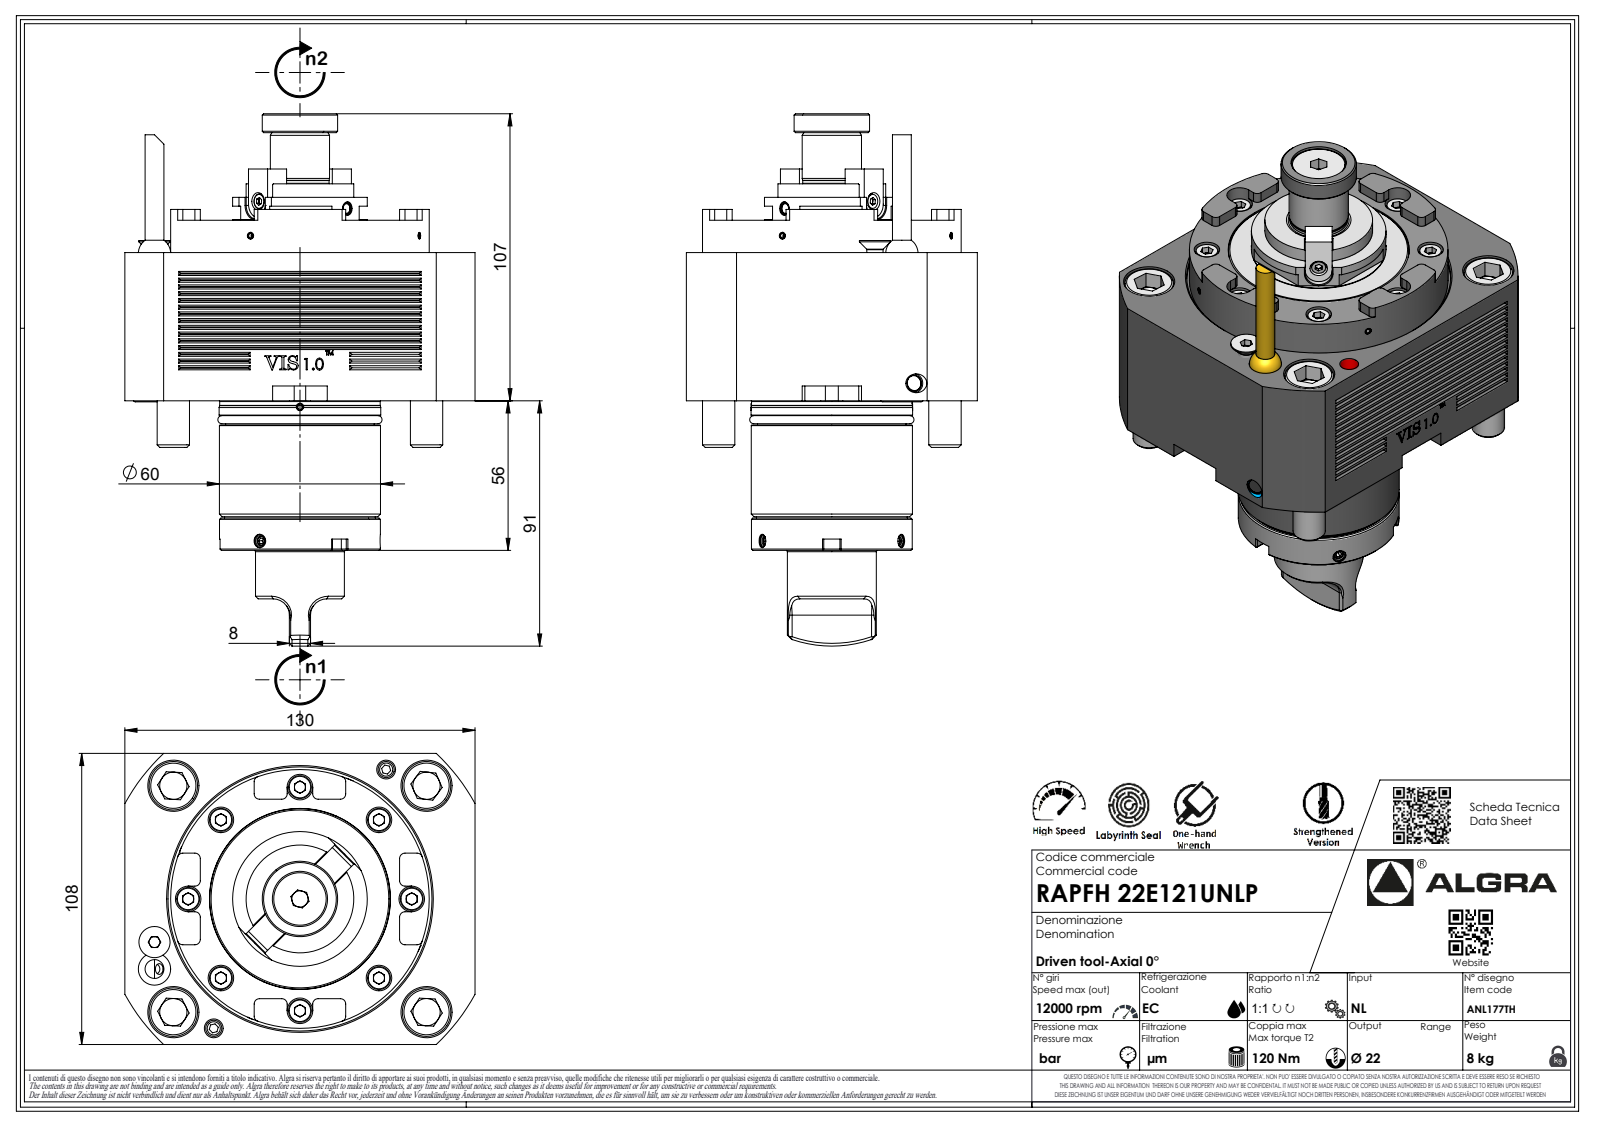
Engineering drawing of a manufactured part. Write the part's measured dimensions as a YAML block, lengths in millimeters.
part_name: "RAPFH22E121UNLP"
step_written_by: "SolidWorks 2023 (AUTOMOTIVE_DESIGN)"
units: millimeters
bodies: {solids: 1, faces: 528, planar: 351, cylindrical: 94, other: 83}
overall_size: [197.5, 130, 108]
volume: 1049000
surface_area: 80060
round_holes:
  - {diameter: 2.1, count: 1}
  - {diameter: 4, count: 1}
round_bosses_or_shafts:
  - {diameter: 12, count: 4}
  - {diameter: 96, count: 1}
  - {diameter: 60, count: 1}
  - {diameter: 50, count: 1}
  - {diameter: 40, count: 1}
  - {diameter: 33, count: 1}
  - {diameter: 28, count: 1}
  - {diameter: 22, count: 1}
partial_cylinders:
  - {radius: 2, count: 25}
  - {radius: 8, count: 8}
  - {radius: 0.33, count: 7}
  - {radius: 0.52, count: 7}
  - {radius: 3.7, count: 7}
  - {radius: 6, count: 6}
  - {radius: 4.75, count: 4}
  - {radius: 5, count: 3}
face_to_face_distances: [55, 108, 12, 67, 130, 55.5, 110.5, 122.5, 5.5, 61.5]
